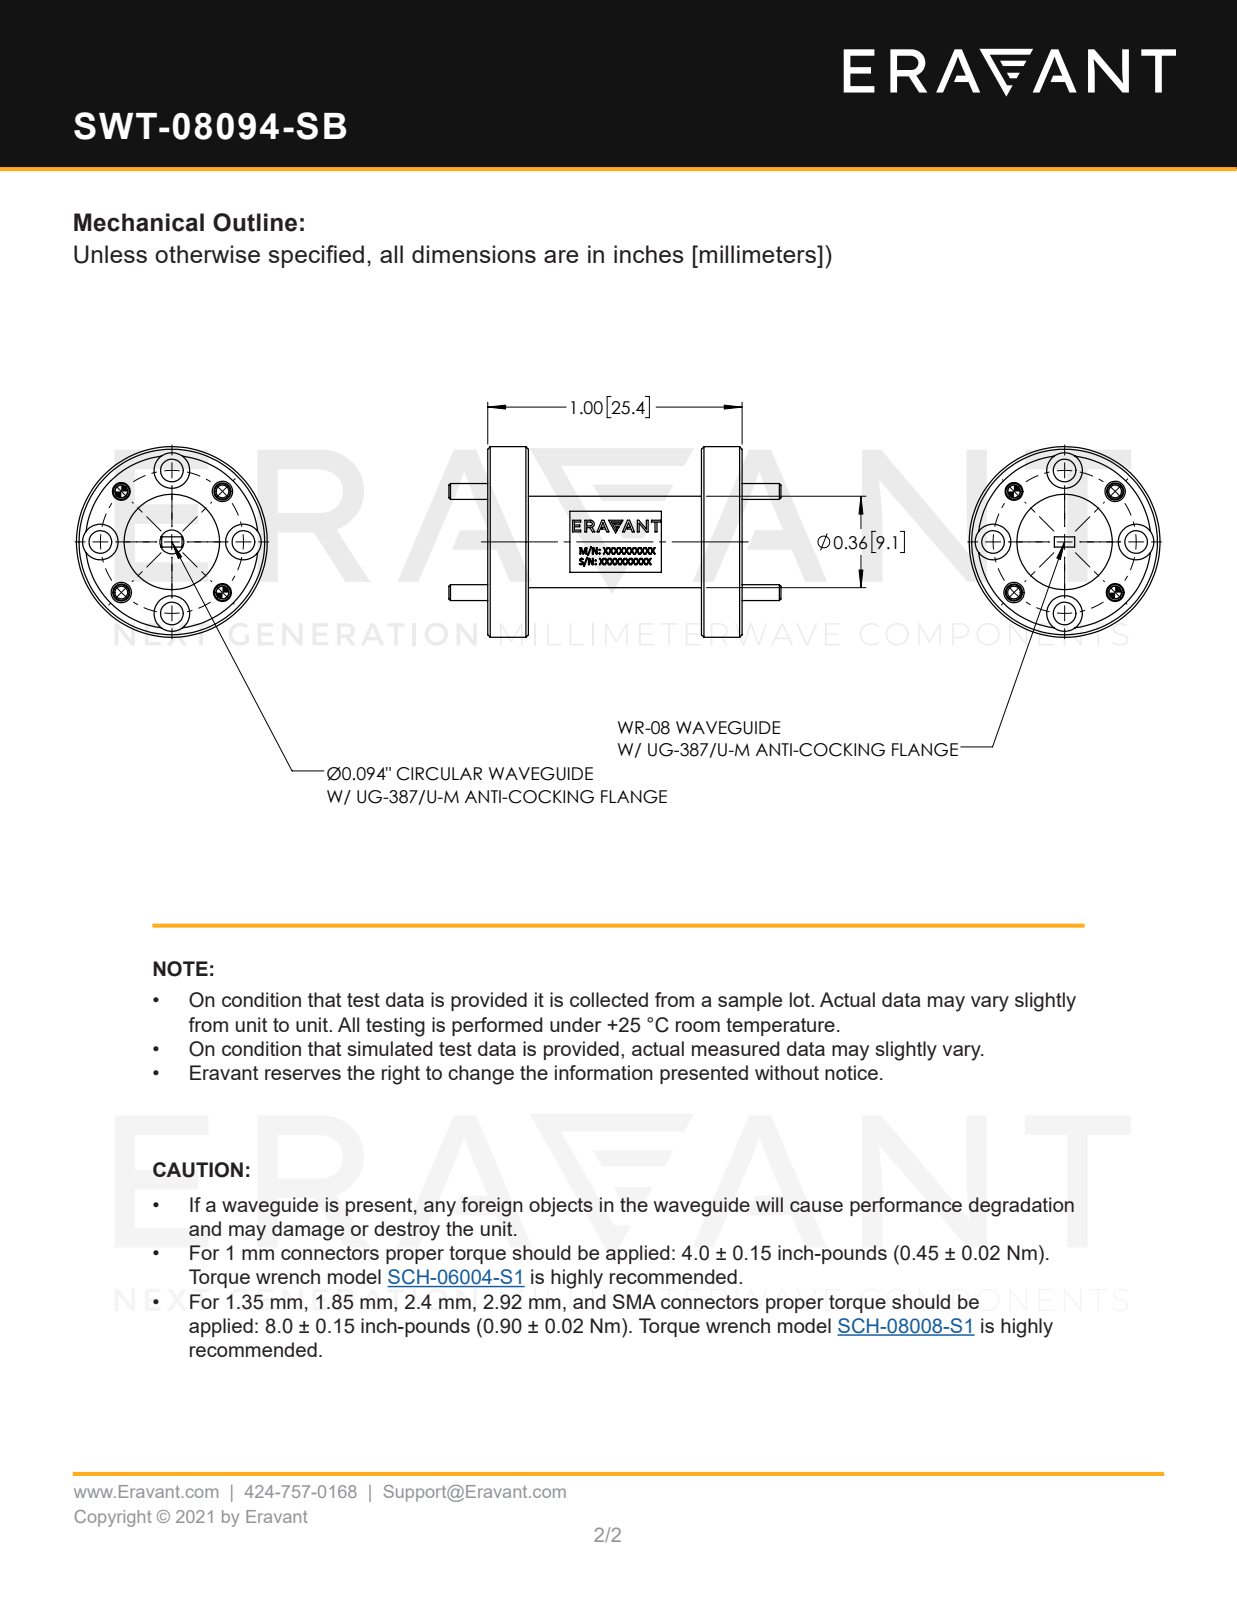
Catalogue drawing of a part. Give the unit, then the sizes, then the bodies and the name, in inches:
Units: inches
Overall size (bounding box): 1.305 × 0.75 × 0.75
Round holes (diameter × count): ⌀0.061 ×4, ⌀0.067 ×4, ⌀0.089 ×4, ⌀0.14 ×4, ⌀0.68 ×1
Round bosses / shafts (diameter × count): ⌀0.063 ×4, ⌀0.75 ×1, ⌀0.375 ×1, ⌀0.375 ×1, ⌀0.36 ×1
Main face-to-face distances: 0.98, 0.02, 0.68, 0.82, 0.14, 0.14, 0.82, 0.96, 0.84, 0.16
Hole centre spacings: 0.215, 0.398, 0.281, 0.519, 0.562, 0.52, 0.281, 0.563
Volume: 0.19 in³ · Surface area: 3.868 in²
Bodies: 5 solids, 148 faces (26 planar, 74 cylindrical, 48 other)
Part name (STEP PRODUCT): SWT-08094-SB
STEP written by: SolidWorks 2021 (CONFIG_CONTROL_DESIGN)
